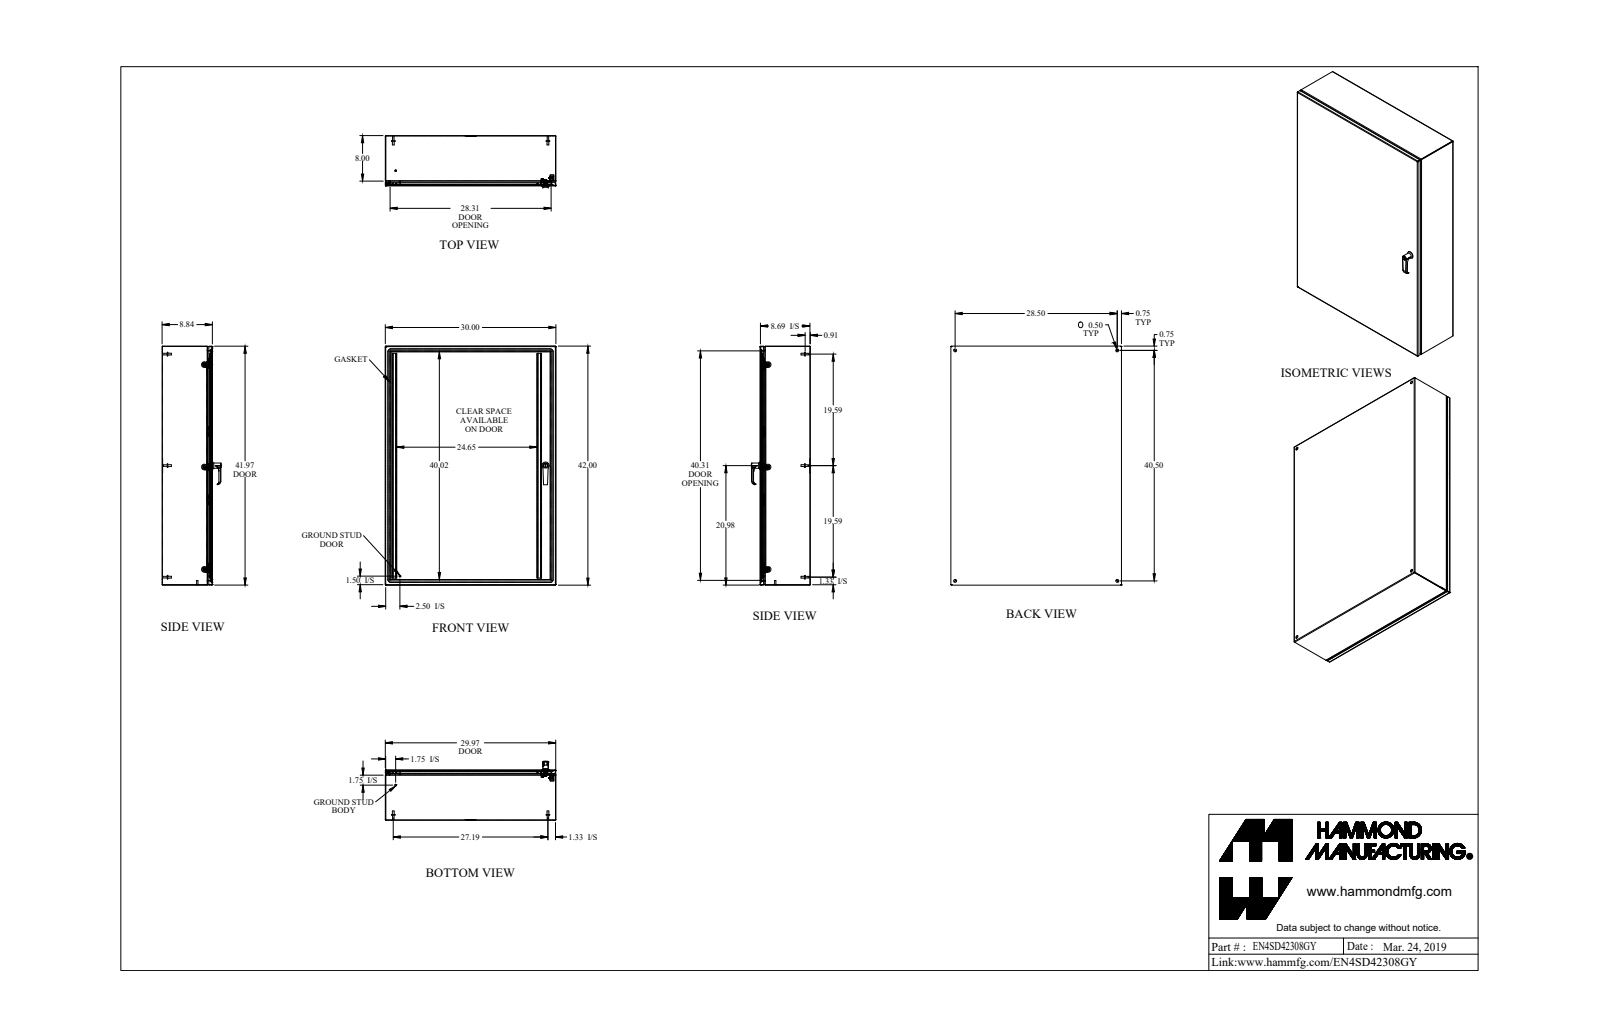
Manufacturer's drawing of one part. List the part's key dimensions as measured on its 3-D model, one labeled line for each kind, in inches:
Part name (STEP PRODUCT): EN4SD42308GY_Default
STEP written by: SolidWorks 2019 (CONFIG_CONTROL_DESIGN)
Units: inches
Bodies: 53 solids, 1457 faces (632 planar, 538 cylindrical, 287 other)
Overall size (bounding box): 42 × 30 × 10.367
Volume: 312.8 in³ · Surface area: 8 671 in²
Round holes (diameter × count): ⌀0.176 ×6, ⌀0.5 ×4, ⌀0.196 ×3, ⌀0.25 ×3, ⌀0.265 ×3, ⌀0.413 ×3, ⌀0.172 ×2, ⌀0.242 ×2, ⌀0.256 ×2, ⌀0.313 ×2, ⌀0.394 ×2, ⌀0.24 ×1
Round bosses / shafts (diameter × count): ⌀0.25 ×7, ⌀0.375 ×6, ⌀0.313 ×6, ⌀0.27 ×6, ⌀0.156 ×6, ⌀0.625 ×4, ⌀1 ×3, ⌀0.63 ×2
Partial cylindrical surfaces — rounded edges, fillets, slot ends (radius × count): R0.036 ×20, R0.108 ×20, R0.03 ×15, R0.043 ×12, R0.081 ×12, R0.006 ×8, R0.04 ×8, R0.062 ×8
Main face-to-face distances: 0.072, 8.765, 8.693, 8.837, 29.928, 41.928, 29.856, 30, 41.856, 42
Hole centre spacings: 0.787, 2.507, 18, 27.52, 28.5, 35.969, 38.25, 40.5
